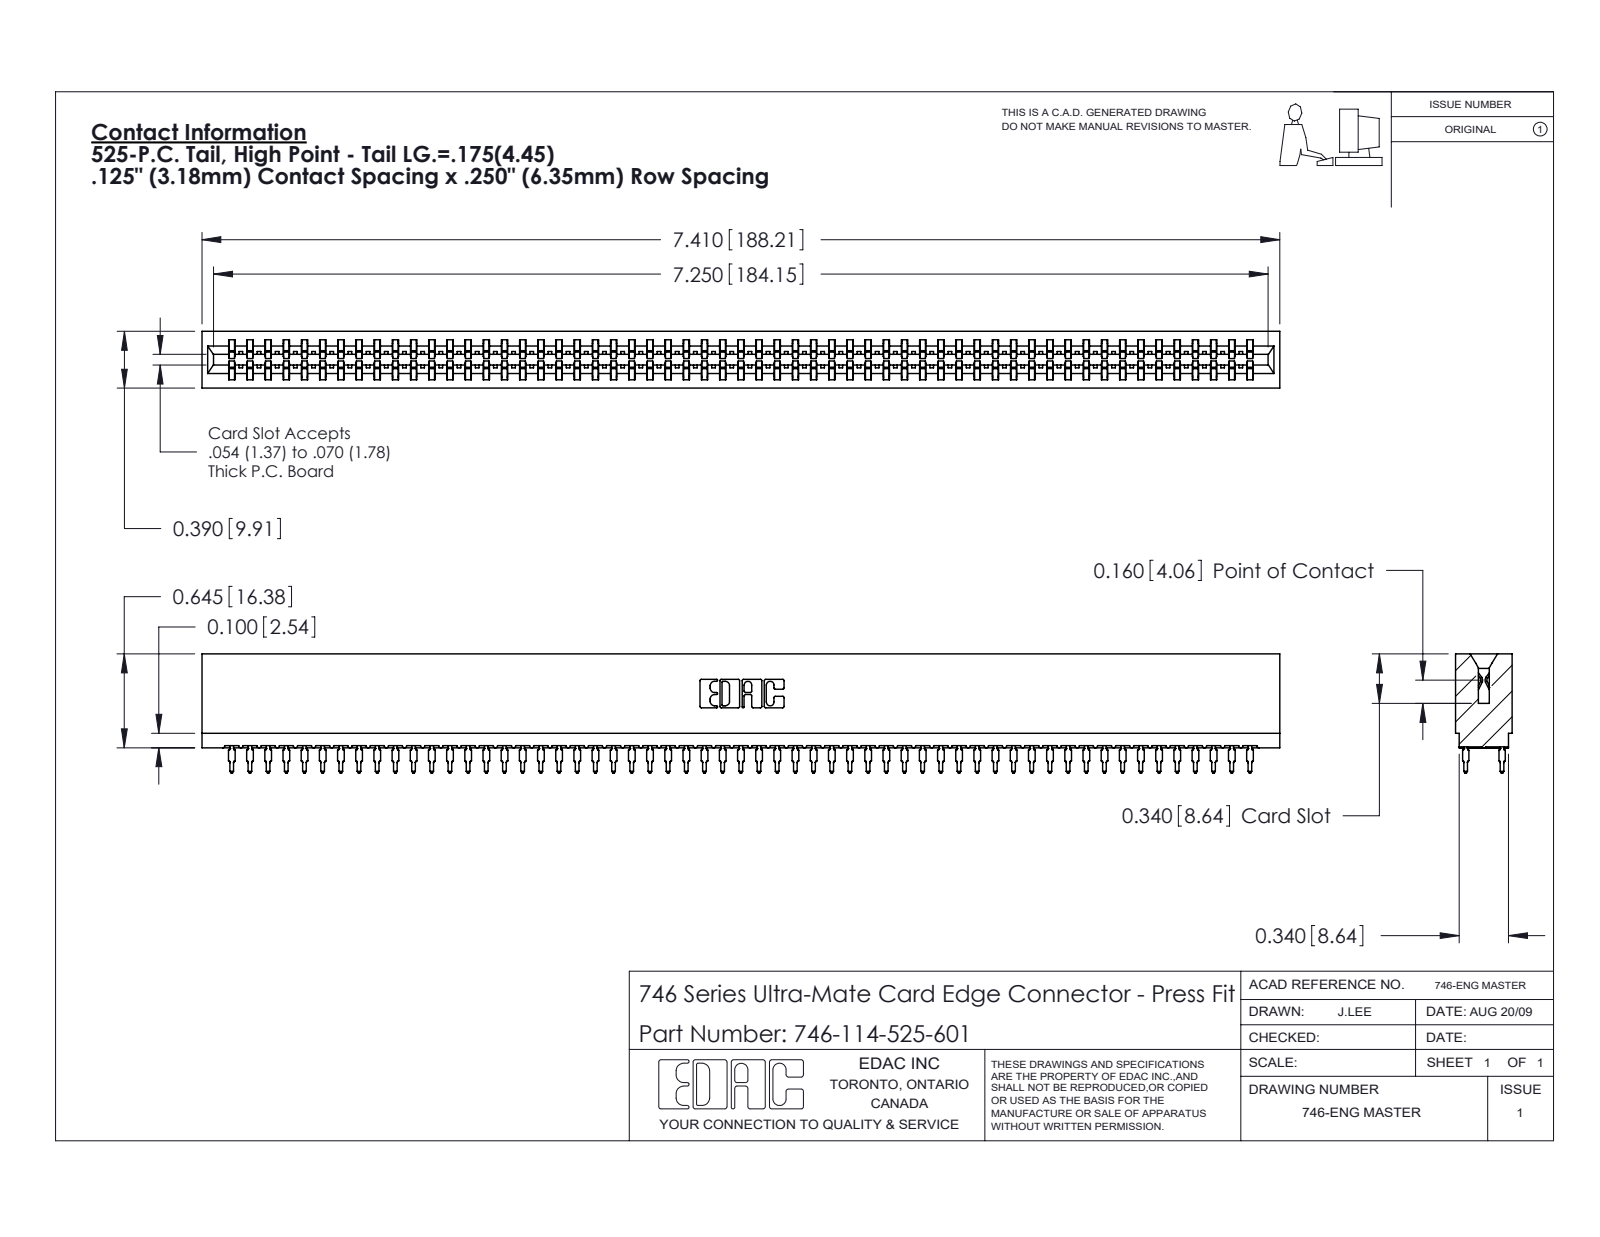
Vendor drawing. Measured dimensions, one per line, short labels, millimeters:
name: 746-292-001_525; 746-114-525-601; 746 Part_.340 Slot Depth - 01
written by: SolidWorks 2020 (CONFIG_CONTROL_DESIGN)
unit: mm
bodies: 115 solids, 10300 faces (5299 planar, 2037 cylindrical, 2964 other)
size: 188.2 × 20.8 × 9.9
volume: 21 500 mm³; area: 31 490 mm²
rounds: 228× R0.5, 58× R0.4, 22× R0.3, 8× R0.1, 8× R0.3, 6× R0.2, 6× R0.8, 3× R0.7
face distances: 1.4, 8.5, 9.9, 0.6, 6.4, 7.8, 7, 2.1, 0.4, 1.5
